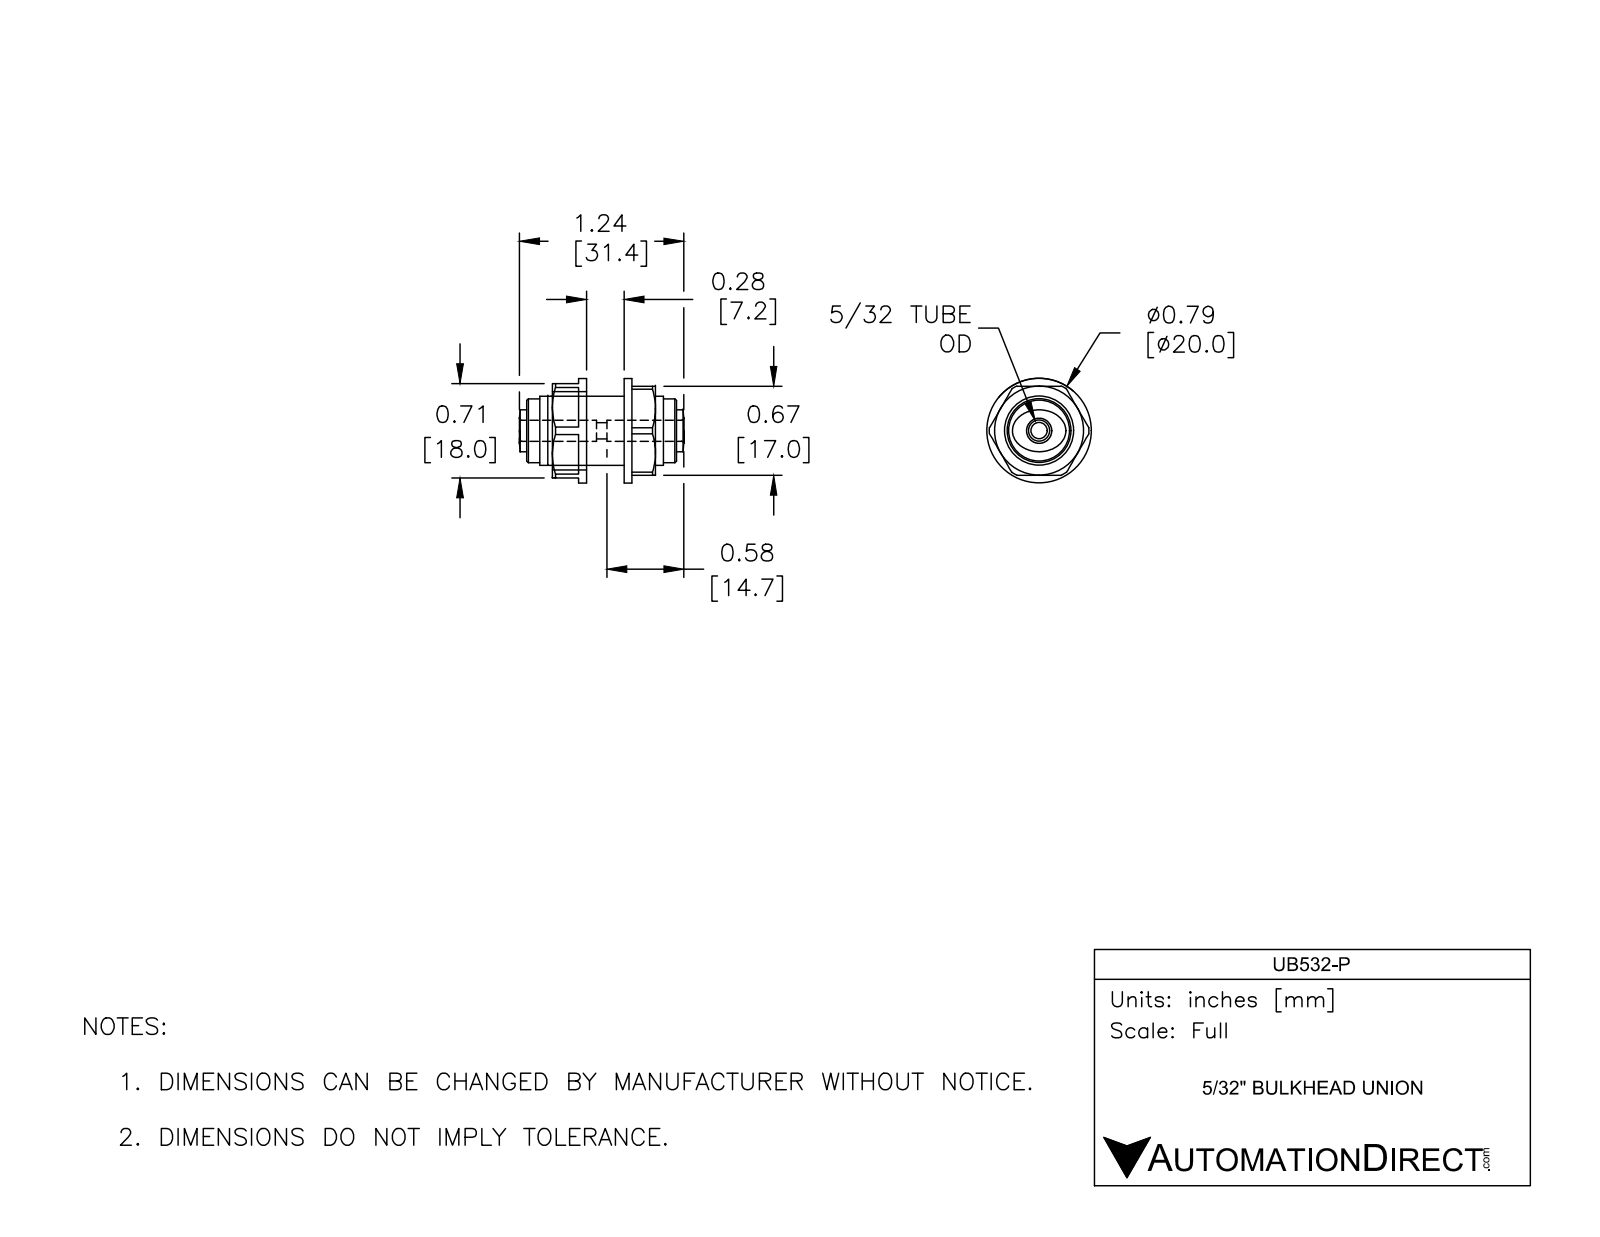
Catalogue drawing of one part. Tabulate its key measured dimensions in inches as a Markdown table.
| quantity | value |
| --- | --- |
| part name | UB532-P |
| STEP written by | SolidWorks 2017 (AUTOMOTIVE_DESIGN) |
| units | inches |
| bodies | 1 solid, 90 faces (31 planar, 29 cylindrical, 30 other) |
| overall size | 1.236 × 0.787 × 0.787 |
| volume | 0.337 in³ |
| surface area | 4.533 in² |
| round holes (diameter × count) | 0.122 × 1, 0.157 × 1, 0.591 × 1 |
| round bosses / shafts (diameter × count) | 0.787 × 1, 0.52 × 1, 0.48 × 1 |
| partial cylindrical surfaces (radius × count) | 0.374 × 1 |
| main face-to-face distances | 0.02, 0.689, 0.52, 0.283, 0.709, 0.059, 0.236, 0.669, 0.094, 0.343 |
